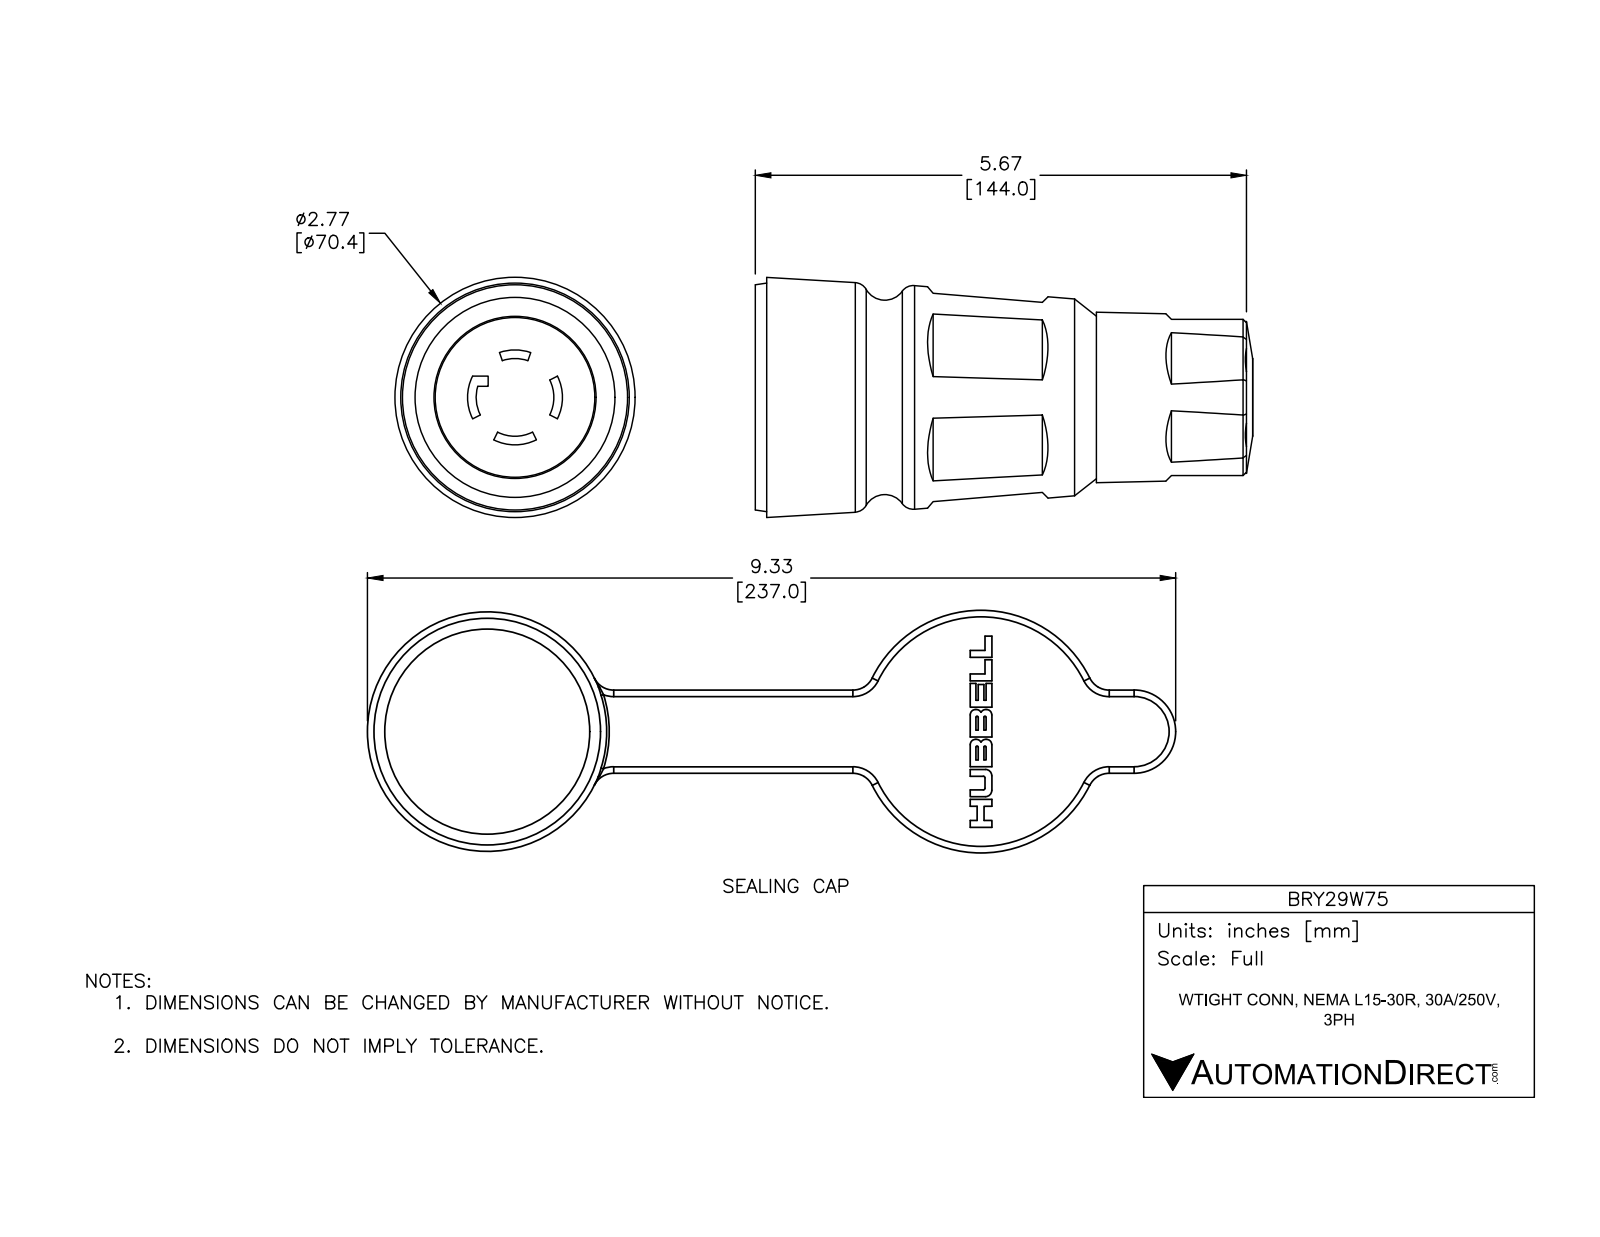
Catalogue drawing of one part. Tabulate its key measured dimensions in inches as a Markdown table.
| quantity | value |
| --- | --- |
| part name | BRY29W75; BRY29W-CAP; BRY29W75-CONNECTOR |
| STEP written by | SolidWorks 2016 (AUTOMOTIVE_DESIGN) |
| units | inches |
| bodies | 5 solids, 183 faces (76 planar, 51 cylindrical, 56 other) |
| overall size | 9.291 × 5.741 × 2.785 |
| volume | 21.54 in³ |
| surface area | 140.8 in² |
| round holes (diameter × count) | 0.807 × 1, 1.752 × 1, 1.87 × 1, 2.008 × 1, 2.283 × 1, 2.307 × 1 |
| round bosses / shafts (diameter × count) | 2.785 × 1, 2.622 × 1, 2.421 × 1, 2.299 × 1, 1.843 × 1, 1.555 × 1 |
| partial cylindrical surfaces (radius × count) | 0.069 × 4, 0.236 × 4, 0.157 × 2, 0.449 × 1, 0.482 × 1, 0.547 × 1 |
| main face-to-face distances | 0.146, 0.468, 0.613, 1.354, 0.887, 0.741, 0.743, 0.276, 0.13, 0.611 |
| hole center spacings | 5.622 |
